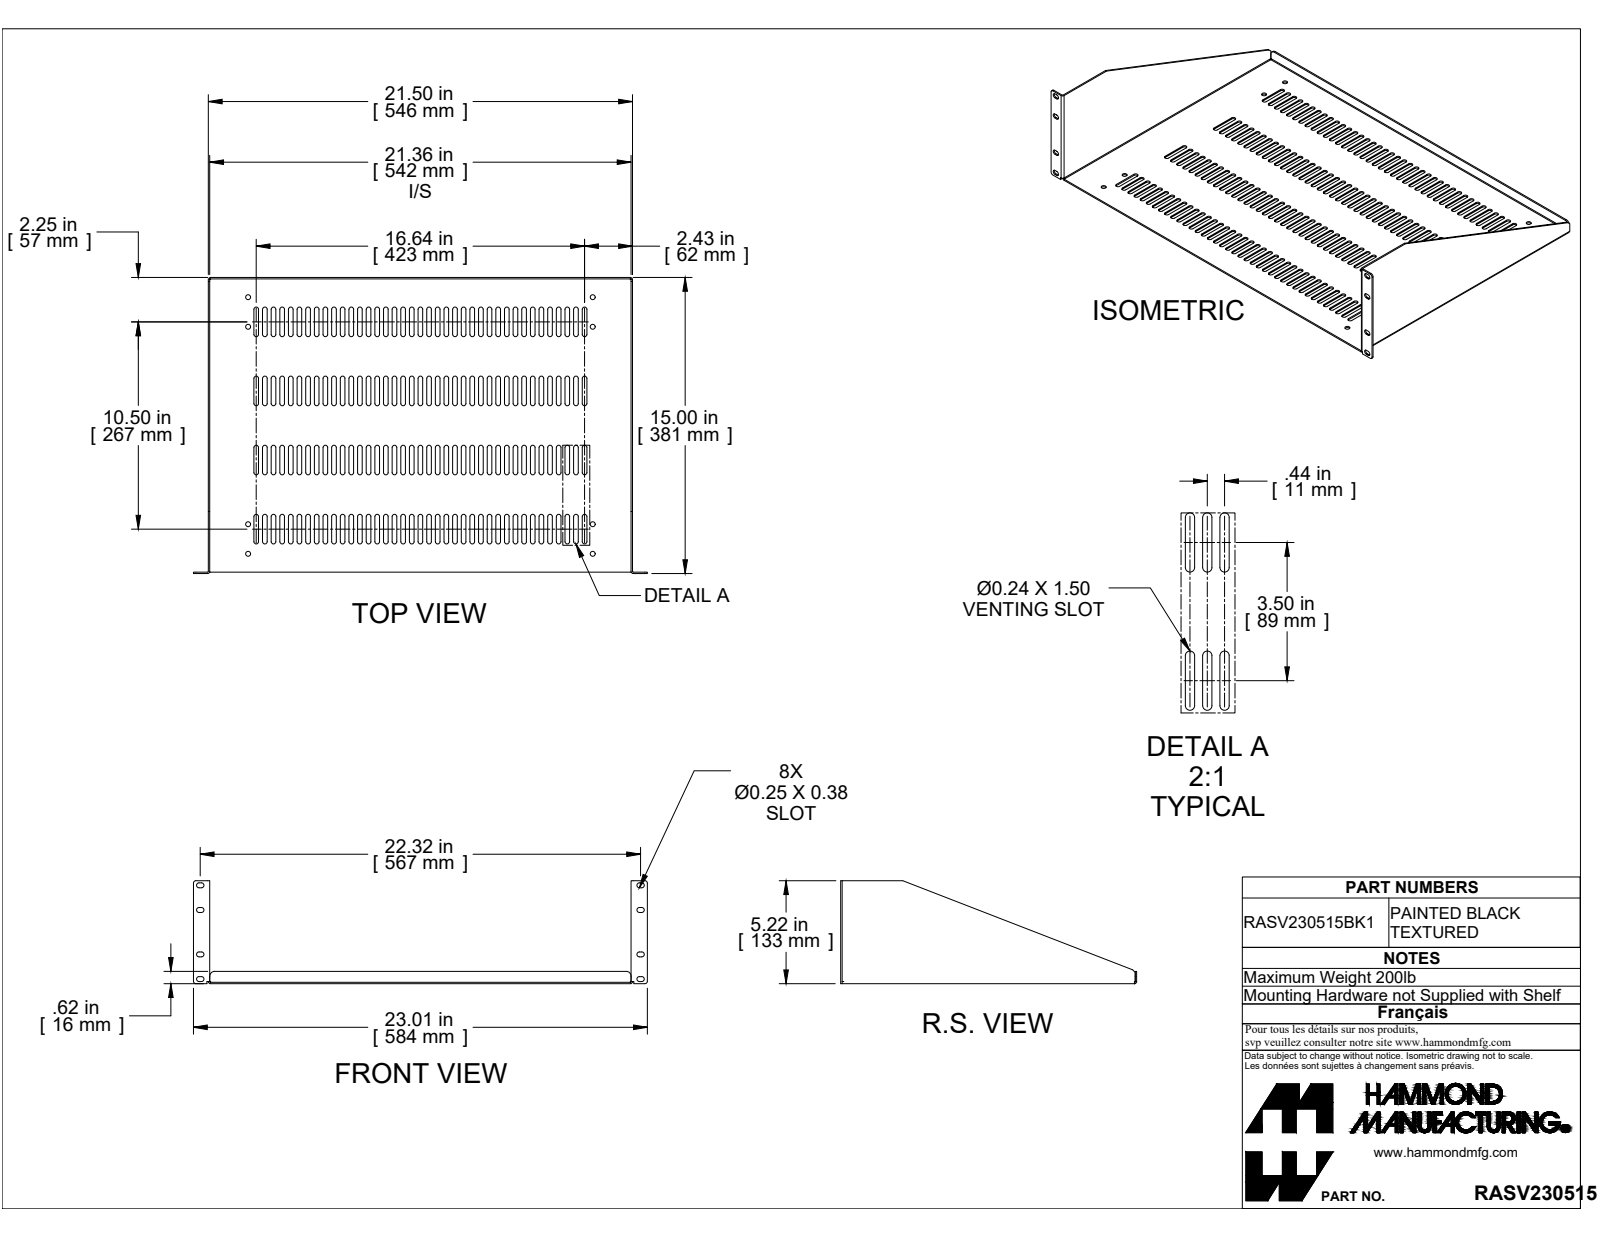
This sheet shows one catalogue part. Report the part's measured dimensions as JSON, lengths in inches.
{"part_name": "RASV230515BK1", "step_written_by": "SolidWorks 2019 (CONFIG_CONTROL_DESIGN)", "units": "inches", "bodies": {"solids": 1, "faces": 728, "planar": 368, "cylindrical": 356, "other": 4}, "overall_size": [23.006, 15, 5.218], "volume_in3": 27.67, "surface_area_in2": 812.9, "round_holes": [[0.25, 8]], "partial_cylinders_radius": [[0.118, 288], [0.117, 24], [0.125, 20], [0.036, 5], [0.108, 5], [0.055, 3], [0.25, 2]], "face_to_face_distances": [0.072, 21.428, 21.356, 21.5, 14.856, 14.928, 0.072, 14.928, 15, 0.876], "hole_center_spacings": [1.5, 11.5, 17.468, 17.532, 20.913, 10, 13, 20.128]}
